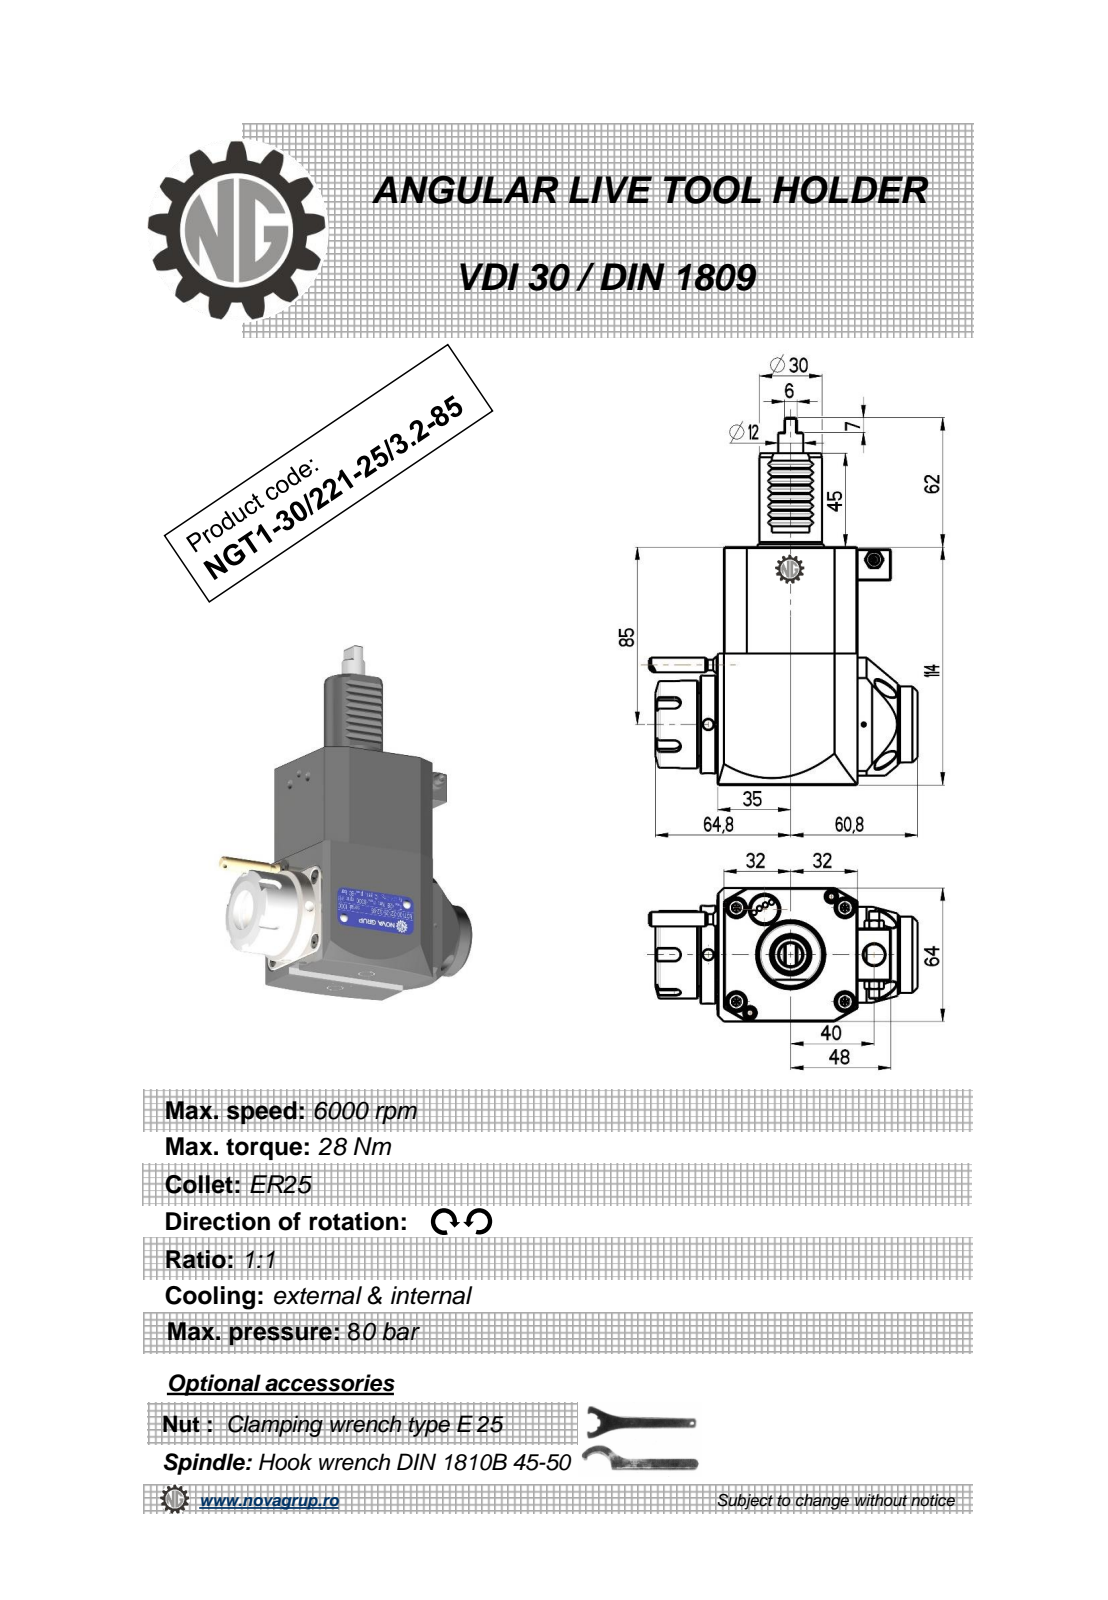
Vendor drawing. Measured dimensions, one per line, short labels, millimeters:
name: NGT1_30_221_25_3_2_85
written by: PRO/ENGINEER BY PARAMETRIC TECHNOLOGY CORPORATION, 2010280 (CONFIG_CONTROL_DESIGN)
unit: mm
bodies: 1 solid, 412 faces (186 planar, 80 cylindrical, 146 other)
size: 176 × 128.63 × 64
volume: 588 665 mm³; area: 54 825 mm²
holes: 2× ⌀5, 1× ⌀2.5, 1× ⌀3, 1× ⌀4.2, 1× ⌀9.5, 1× ⌀10, 1× ⌀20.3
bosses: 2× ⌀5, 1× ⌀47, 1× ⌀42, 1× ⌀36.5, 1× ⌀35, 1× ⌀30, 1× ⌀12, 1× ⌀8.96
rounds: 12× R0.26, 8× R0.3, 5× R3, 2× R0.8, 2× R160, 1× R32
face distances: 64, 114, 0.5, 3.2, 67.2, 76.42, 67, 3, 7.5, 96
hole spacings: 33.19, 50.92, 76.5, 79.45, 112.04
